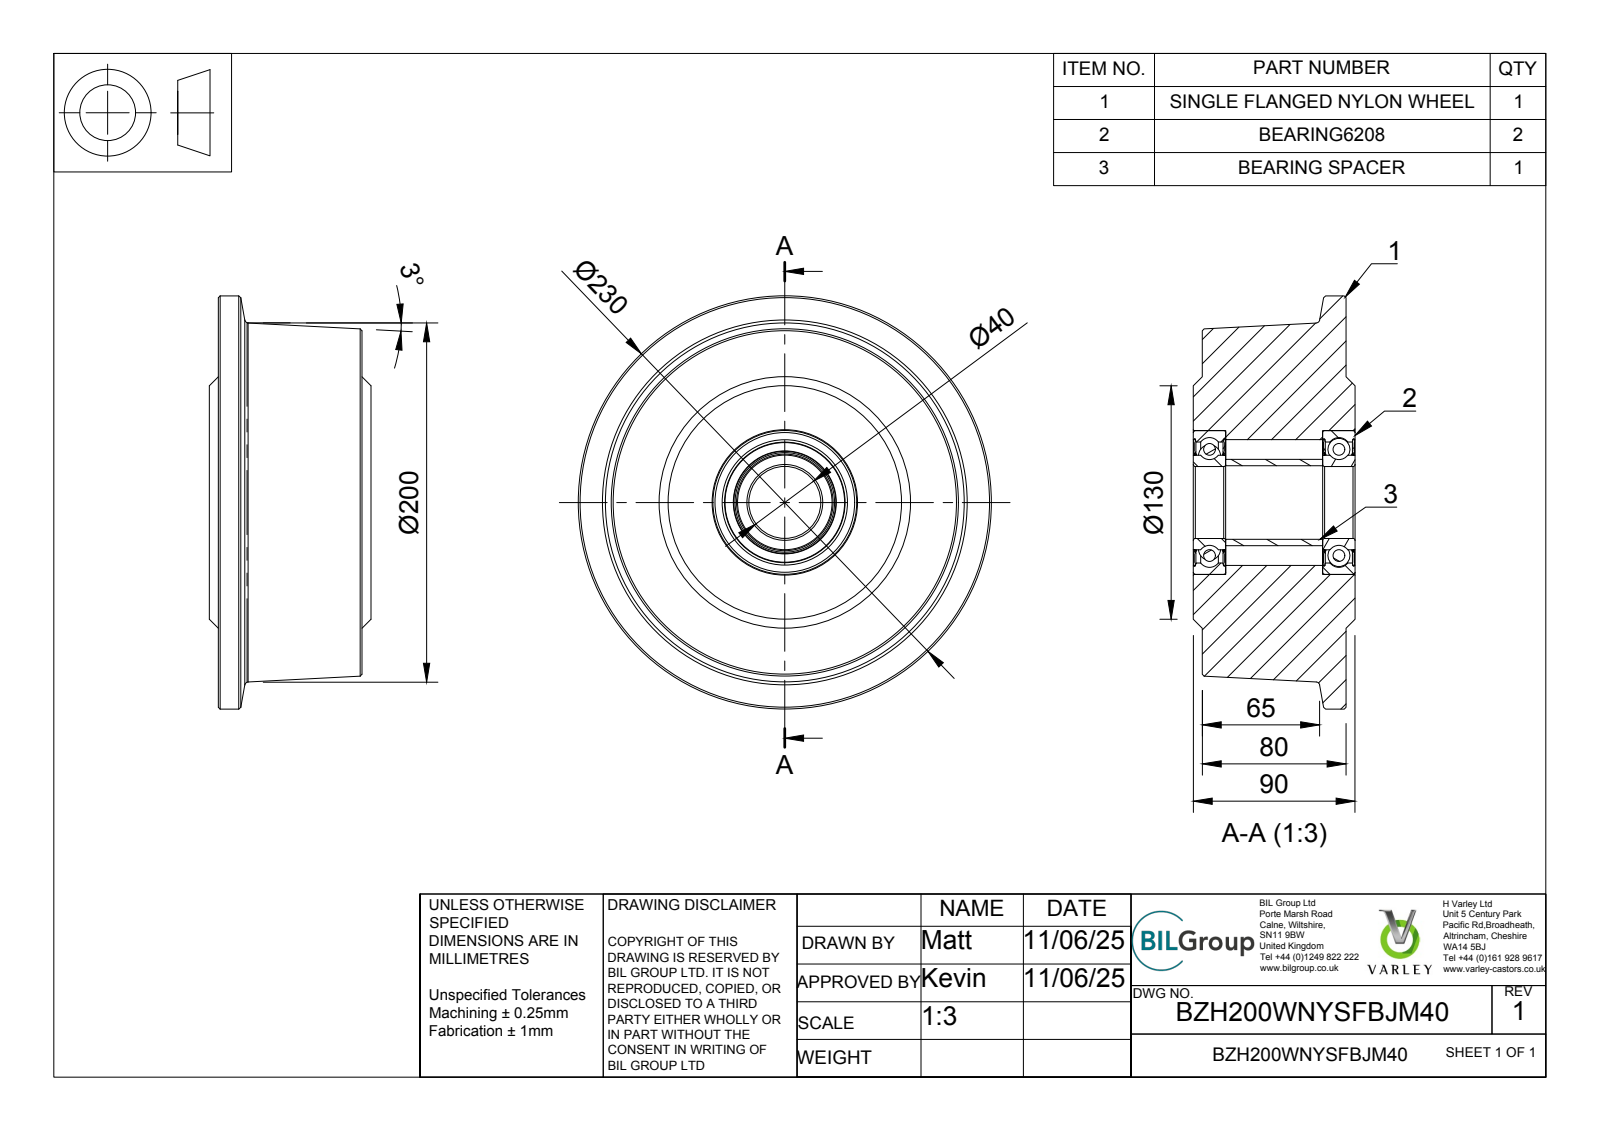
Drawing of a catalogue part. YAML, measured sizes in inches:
part_name: "BZH200WNYSFBJM40 v2; BZH200WNYSFBJM40; skf_bearing_6208-2rs1_2 v1; skf_bearing_6208-2rs1_2 v1 (1) (+1 more)"
step_written_by: "Autodesk Translation Framework v14.10.0.0 (AUTOMOTIVE_DESIGN)"
units: inches
bodies: {solids: 12, faces: 160, planar: 32, cylindrical: 26, other: 102}
overall_size: [9.055, 9.055, 3.543]
volume: 150
surface_area: 344.2
round_holes:
  - {diameter: 1.575, count: 1}
  - {diameter: 1.614, count: 1}
  - {diameter: 2.069, count: 1}
  - {diameter: 2.654, count: 1}
  - {diameter: 2.748, count: 1}
  - {diameter: 2.756, count: 1}
  - {diameter: 3.15, count: 1}
round_bosses_or_shafts:
  - {diameter: 9.055, count: 1}
  - {diameter: 2.071, count: 1}
  - {diameter: 1.89, count: 1}
face_to_face_distances: [0.197, 3.346, 3.15, 3.543, 2.835, 0.69, 0.709, 0.512, 2.638, 0.057]
